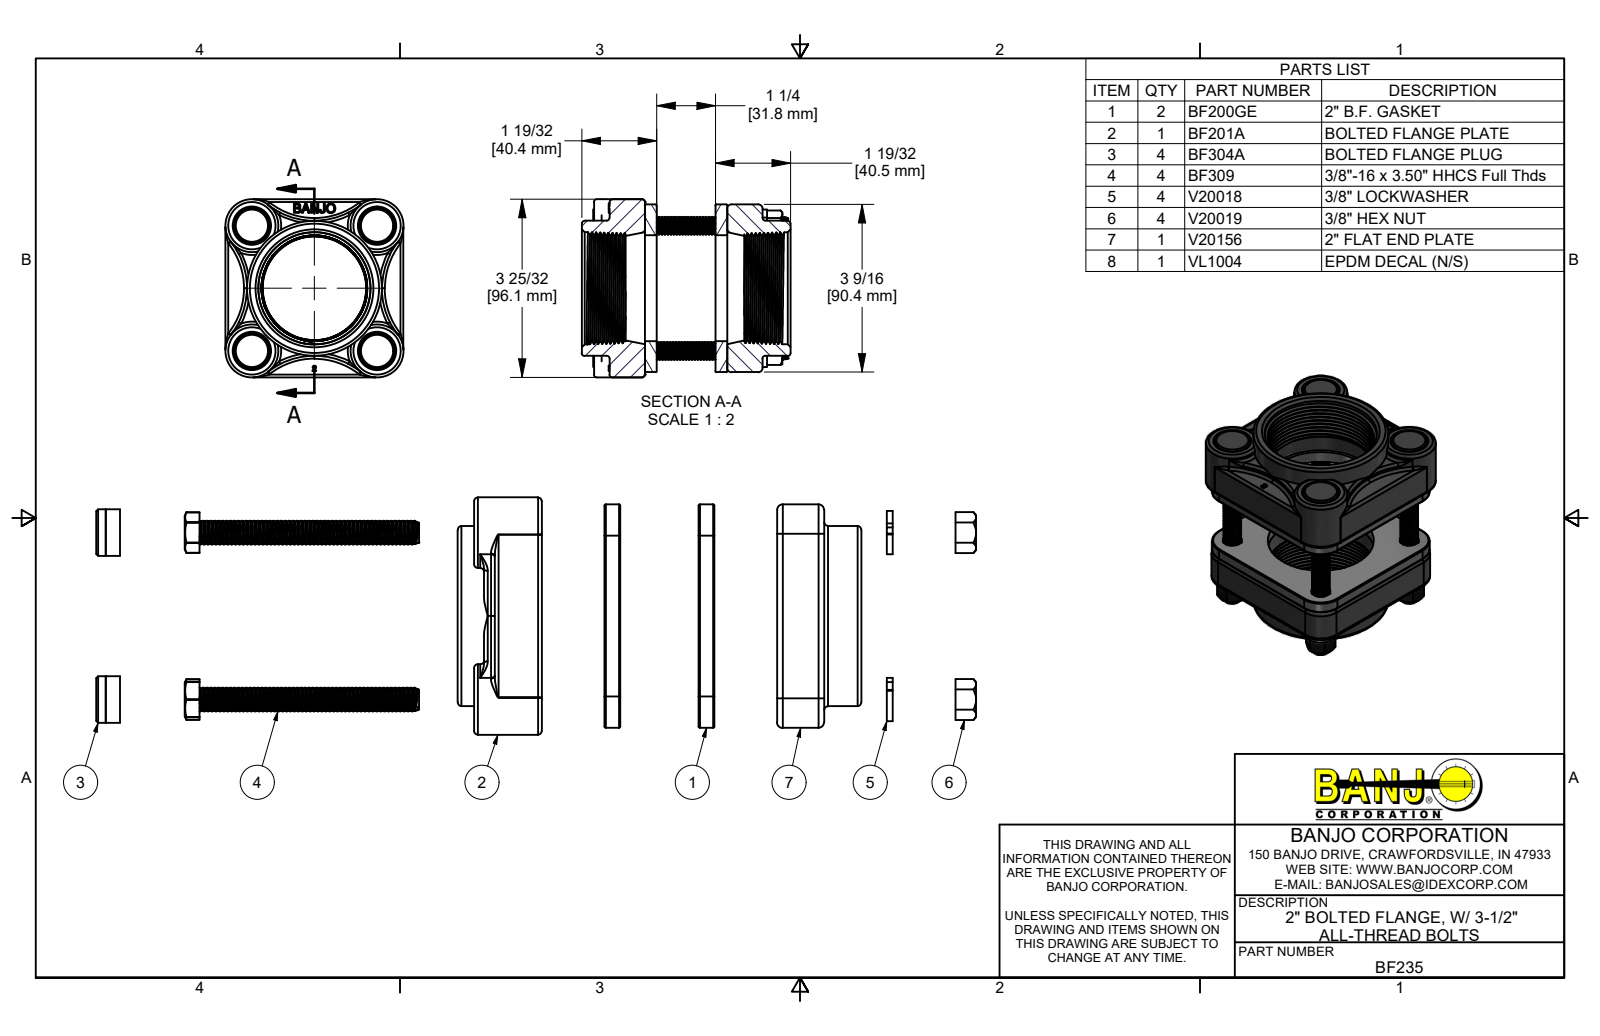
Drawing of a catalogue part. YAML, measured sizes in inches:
part_name: "BF235; BF201A; V20156; V20018 (+4 more)"
step_written_by: "Autodesk Inventor 2019 (AUTOMOTIVE_DESIGN)"
units: inches
bodies: {solids: 20, faces: 1750, planar: 307, cylindrical: 664, other: 779}
overall_size: [38.352, 3.784, 3.784]
volume: 22.61
surface_area: 468.4
round_holes:
  - {diameter: 0.307, count: 4}
  - {diameter: 0.38, count: 4}
  - {diameter: 0.385, count: 4}
  - {diameter: 0.406, count: 4}
  - {diameter: 0.41, count: 4}
  - {diameter: 0.715, count: 4}
  - {diameter: 0.75, count: 4}
  - {diameter: 2.25, count: 1}
round_bosses_or_shafts:
  - {diameter: 0.324, count: 220}
  - {diameter: 1.125, count: 4}
  - {diameter: 0.742, count: 4}
  - {diameter: 0.687, count: 4}
  - {diameter: 0.375, count: 4}
  - {diameter: 2.87, count: 1}
partial_cylinders:
  - {radius: 0.02, count: 16}
  - {radius: 0.06, count: 16}
  - {radius: 0.09, count: 8}
  - {radius: 0.162, count: 8}
  - {radius: 0.322, count: 4}
  - {radius: 0.47, count: 4}
  - {radius: 0.5, count: 4}
  - {radius: 1.6, count: 4}
face_to_face_distances: [0.25, 1.5, 1.75, 1.25, 0.111, 3.671, 0.75, 1, 2.25, 2.5]
hole_center_spacings: [1.88, 2.659, 3.761]
